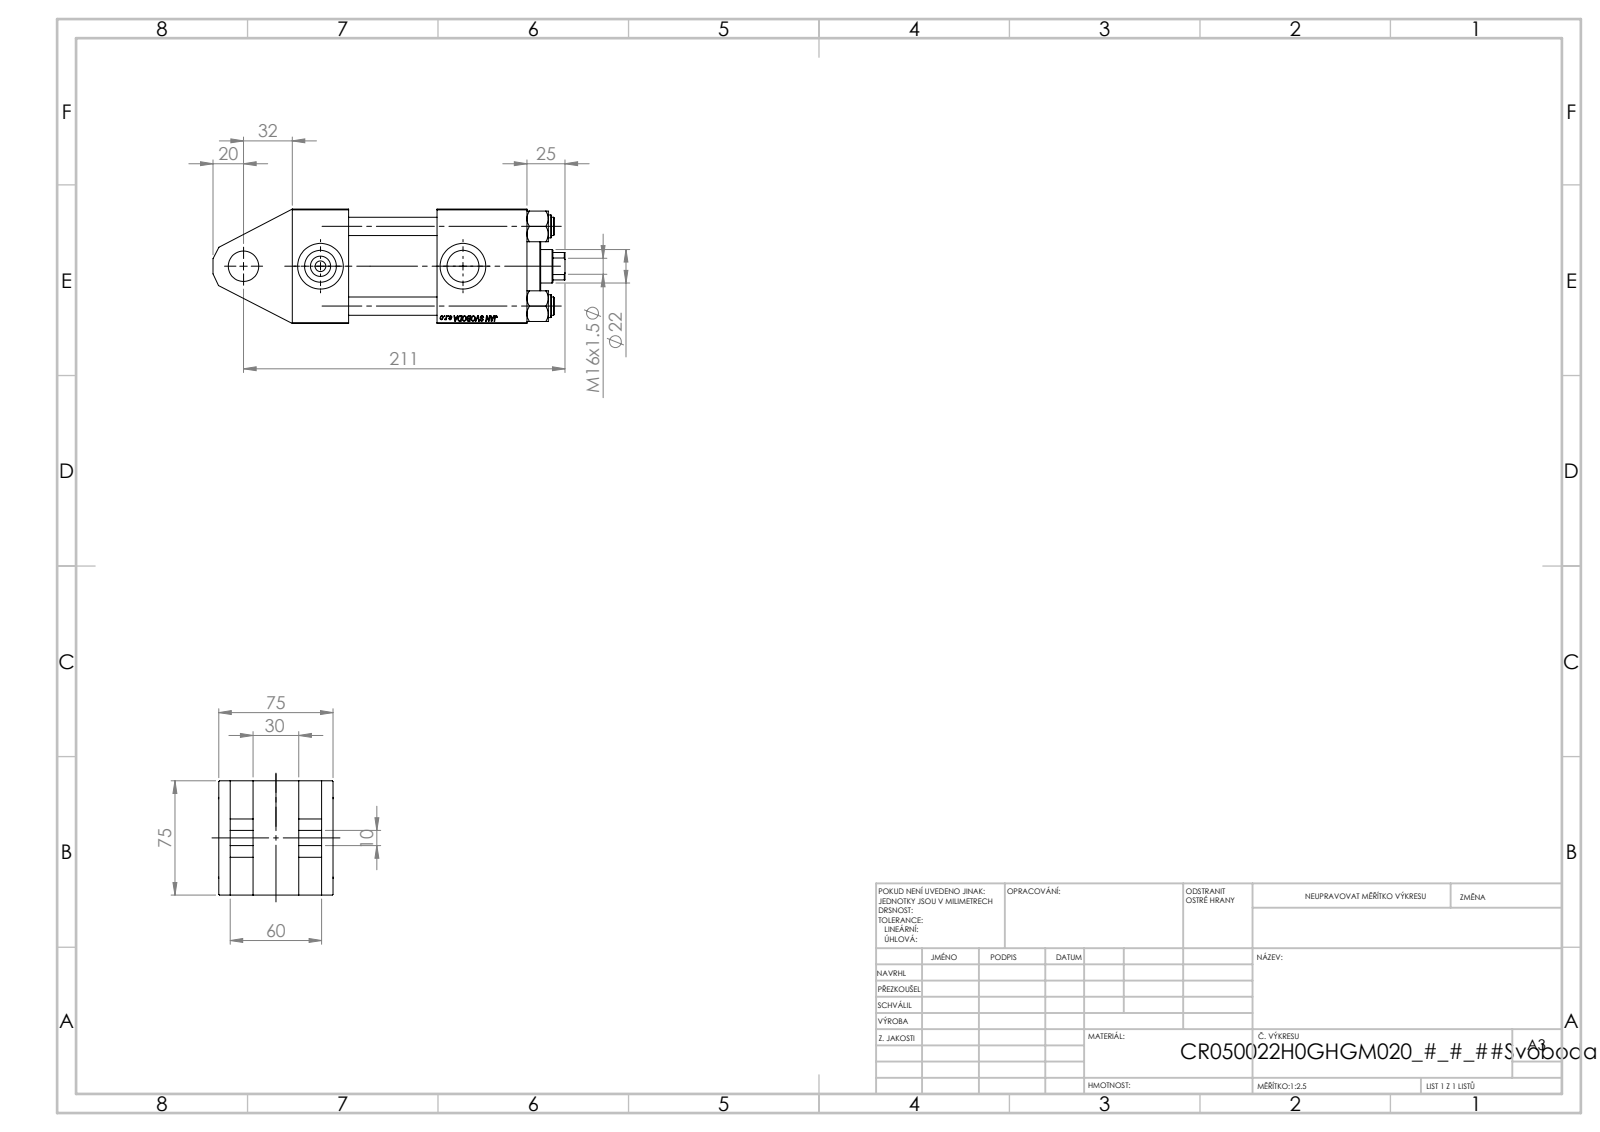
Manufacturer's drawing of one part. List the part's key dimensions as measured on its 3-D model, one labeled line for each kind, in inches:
Part name (STEP PRODUCT): V215CR_TYCINKA_H; NUT_M5_H; V215_VC_A; V215CR_H_Body (+1 more)
STEP written by: SolidWorks 2019 (CONFIG_CONTROL_DESIGN)
Units: inches
Bodies: 11 solids, 1129 faces (518 planar, 83 cylindrical, 528 other)
Overall size (bounding box): 9.094 × 2.974 × 2.953
Volume: 44.8 in³ · Surface area: 252.4 in²
Round holes (diameter × count): ⌀0.472 ×4, ⌀0.276 ×2, ⌀0.825 ×2, ⌀1.181 ×2, ⌀0.413 ×1, ⌀0.787 ×1, ⌀0.866 ×1, ⌀0.984 ×1, ⌀1.614 ×1, ⌀1.969 ×1, ⌀2.087 ×1
Round bosses / shafts (diameter × count): ⌀0.591 ×4, ⌀2.205 ×1, ⌀1.339 ×1
Partial cylindrical surfaces — rounded edges, fillets, slot ends (radius × count): R0.413 ×1
Main face-to-face distances: 2.953, 4.606, 2.657, 0.295, 1.772, 0.886, 2.067, 0.591, 3.74, 1.457
Hole centre spacings: 1.456, 2.059, 2.912, 1.988, 3.681, 5.669
